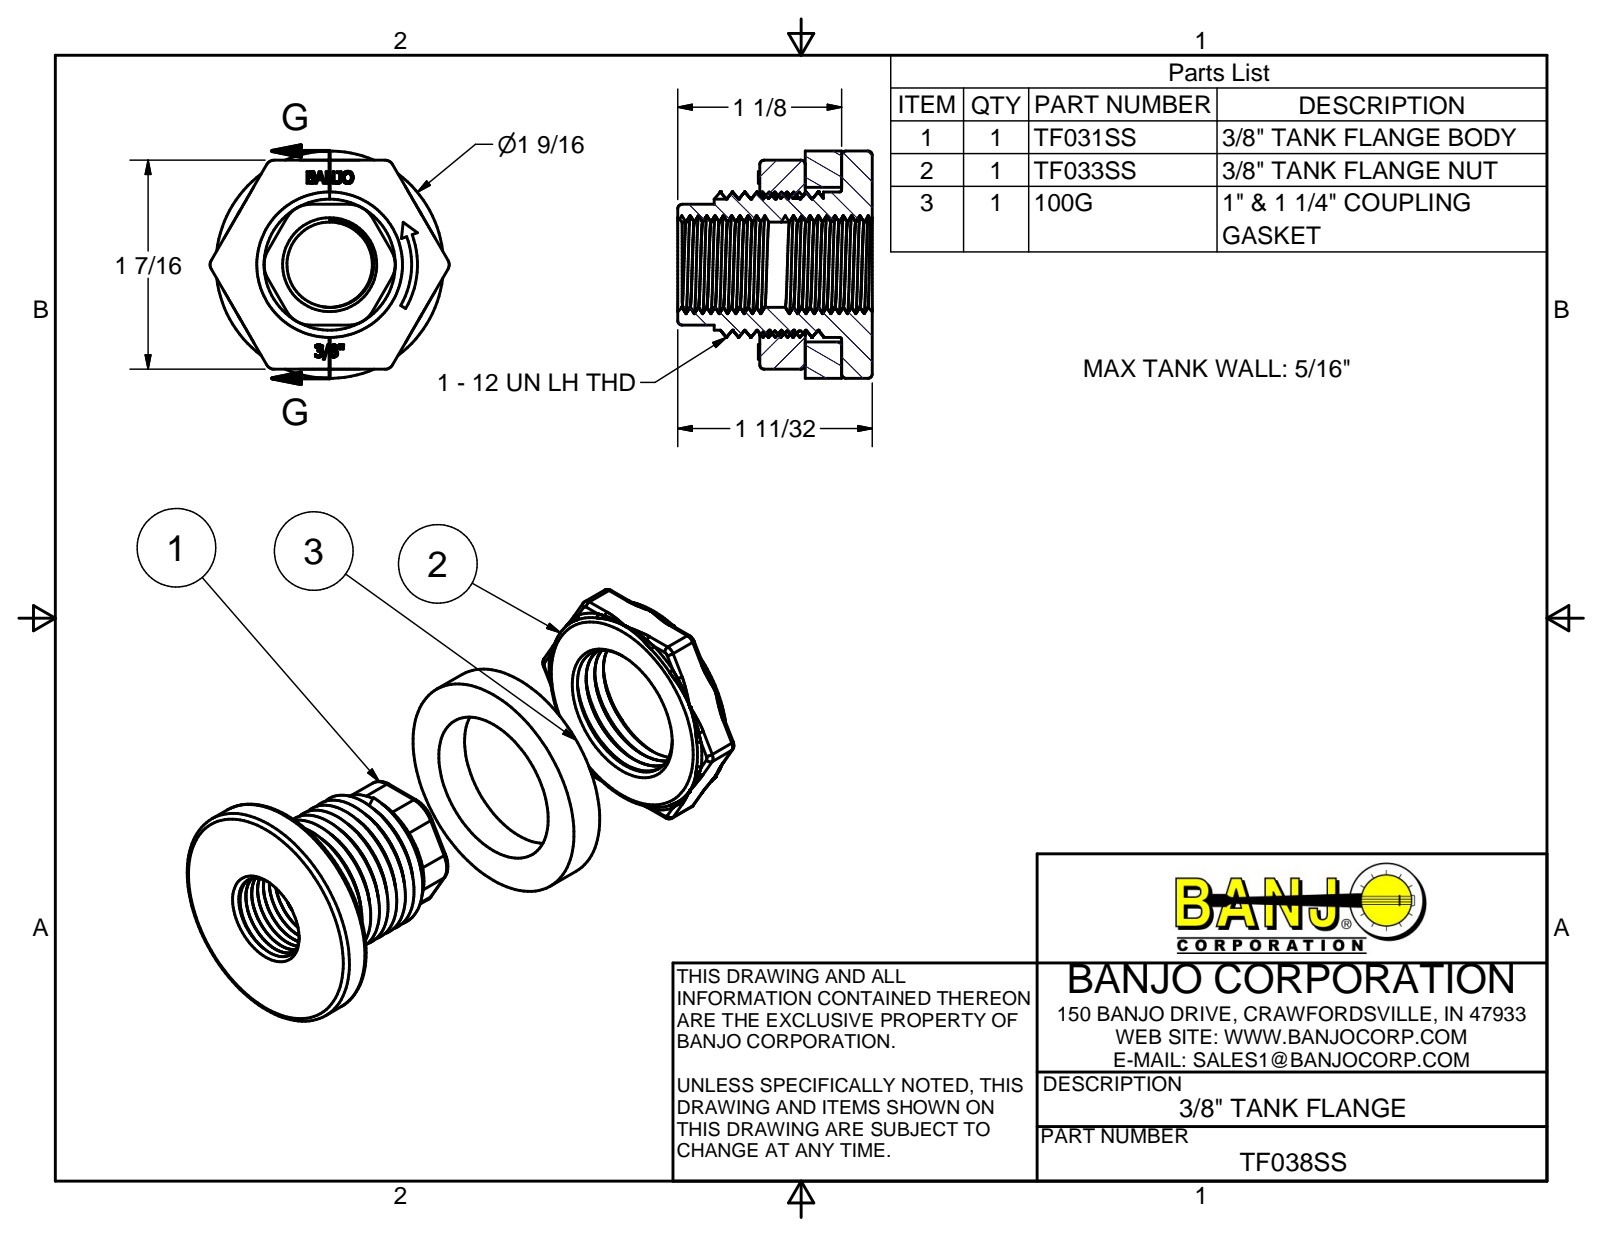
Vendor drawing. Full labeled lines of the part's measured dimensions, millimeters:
Part name (STEP PRODUCT): TF038SS; TF031SS; TF033SS; 100G
STEP written by: Autodesk Inventor 2013 (AUTOMOTIVE_DESIGN)
Units: millimetres
Bodies: 3 solids, 423 faces (126 planar, 83 cylindrical, 214 other)
Overall size (bounding box): 41.7 × 39.7 × 33.9
Volume: 22 060 mm³ · Surface area: 14 140 mm²
Round holes (diameter × count): ⌀14.9 ×1, ⌀23.1 ×1, ⌀27 ×1
Round bosses / shafts (diameter × count): ⌀39.7 ×1, ⌀25.4 ×1, ⌀22.9 ×1
Partial cylindrical surfaces — rounded edges, fillets, slot ends (radius × count): R0.8 ×18, R1.5 ×6, R4.8 ×6, R14.3 ×1, R15.3 ×1, R18.3 ×1
Main face-to-face distances: 6.4, 5.3, 11.7, 14.3, 8, 19.6, 36.5, 7.7, 28.8, 22.2
